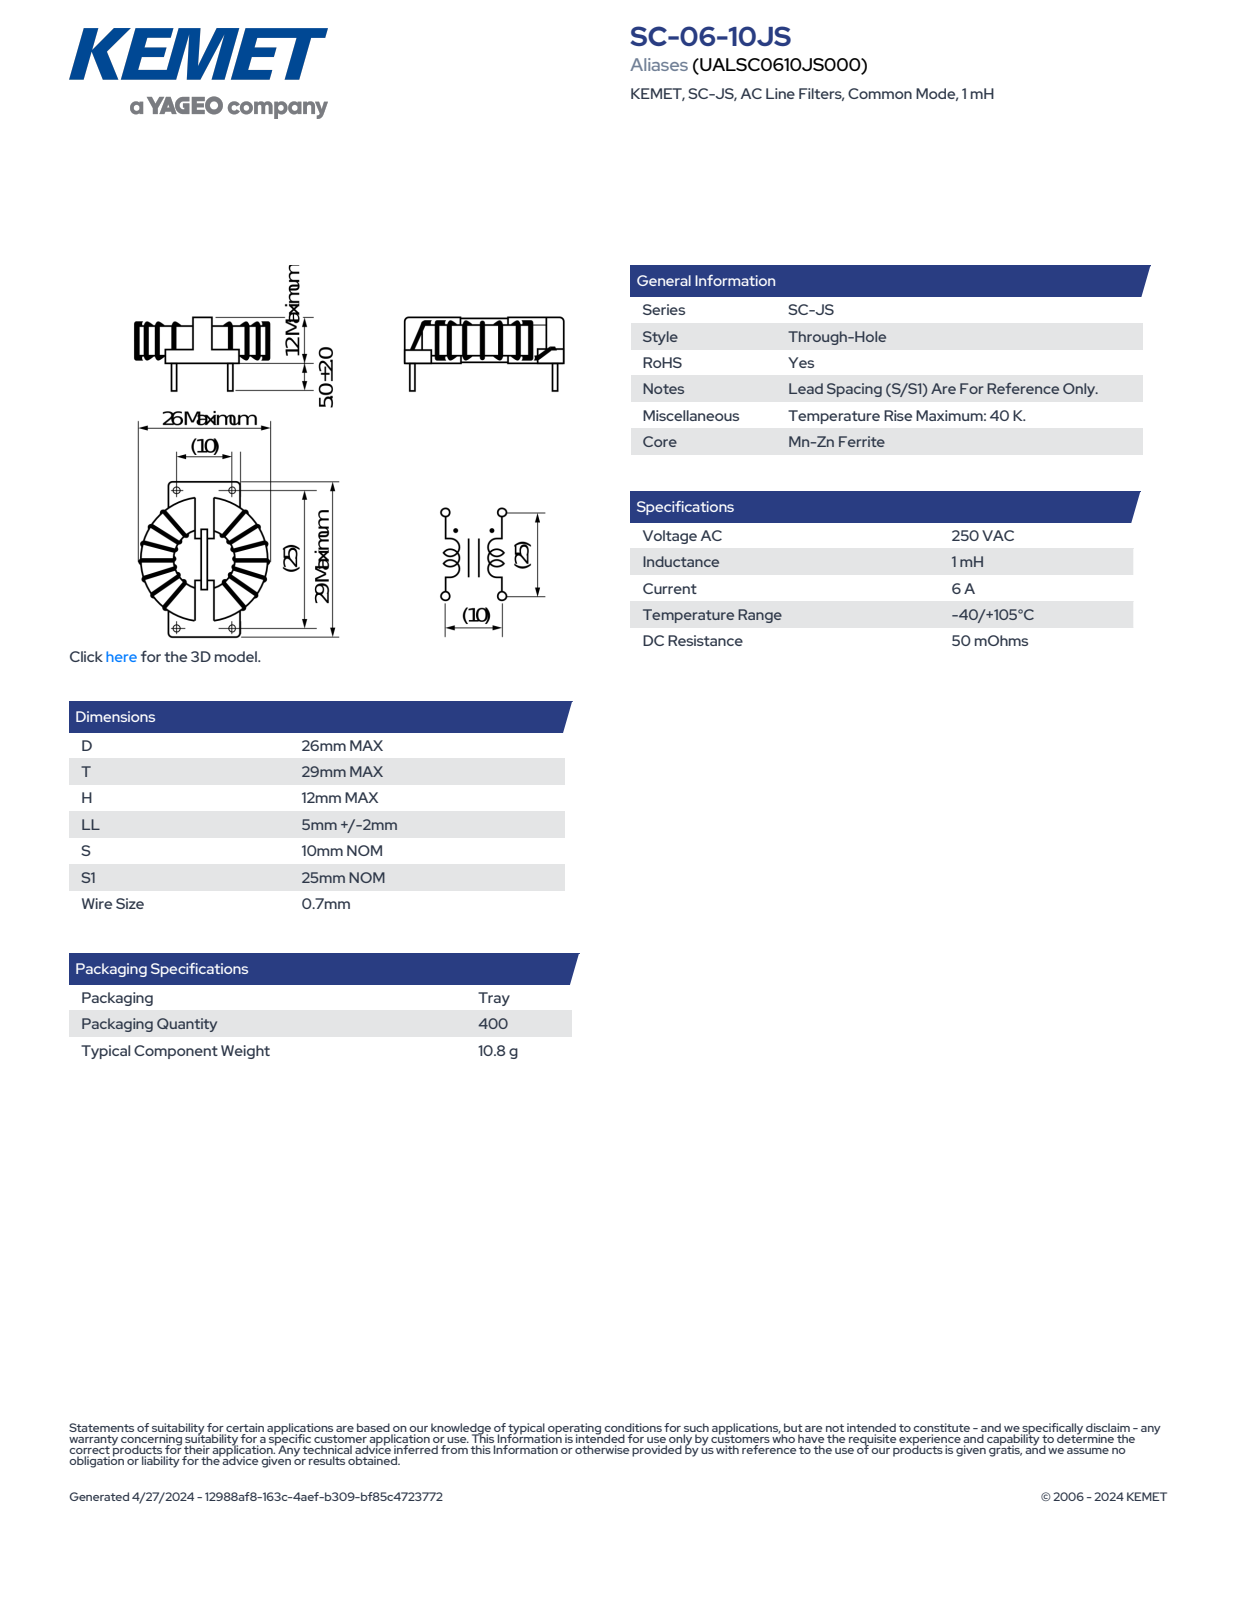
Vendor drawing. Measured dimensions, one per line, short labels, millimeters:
name: SC-06-10JS
written by: SolidWorks 2018 (AUTOMOTIVE_DESIGN)
unit: mm
bodies: 1 solid, 339 faces (142 planar, 123 cylindrical, 74 other)
size: 29 × 26 × 15.35
volume: 4 150 mm³; area: 3 296 mm²
holes: 2× ⌀1.6
bosses: 10× ⌀0.7, 2× ⌀1.5
rounds: 14× R0.2, 12× R0.35, 4× R0.3, 4× R0.7, 4× R1.5, 1× R4, 1× R4.97, 1× R5.38
face distances: 2.15, 1.05, 8.62, 1.4, 10.02, 3.2, 1.1, 1.15, 1, 4.15
hole spacings: 25
